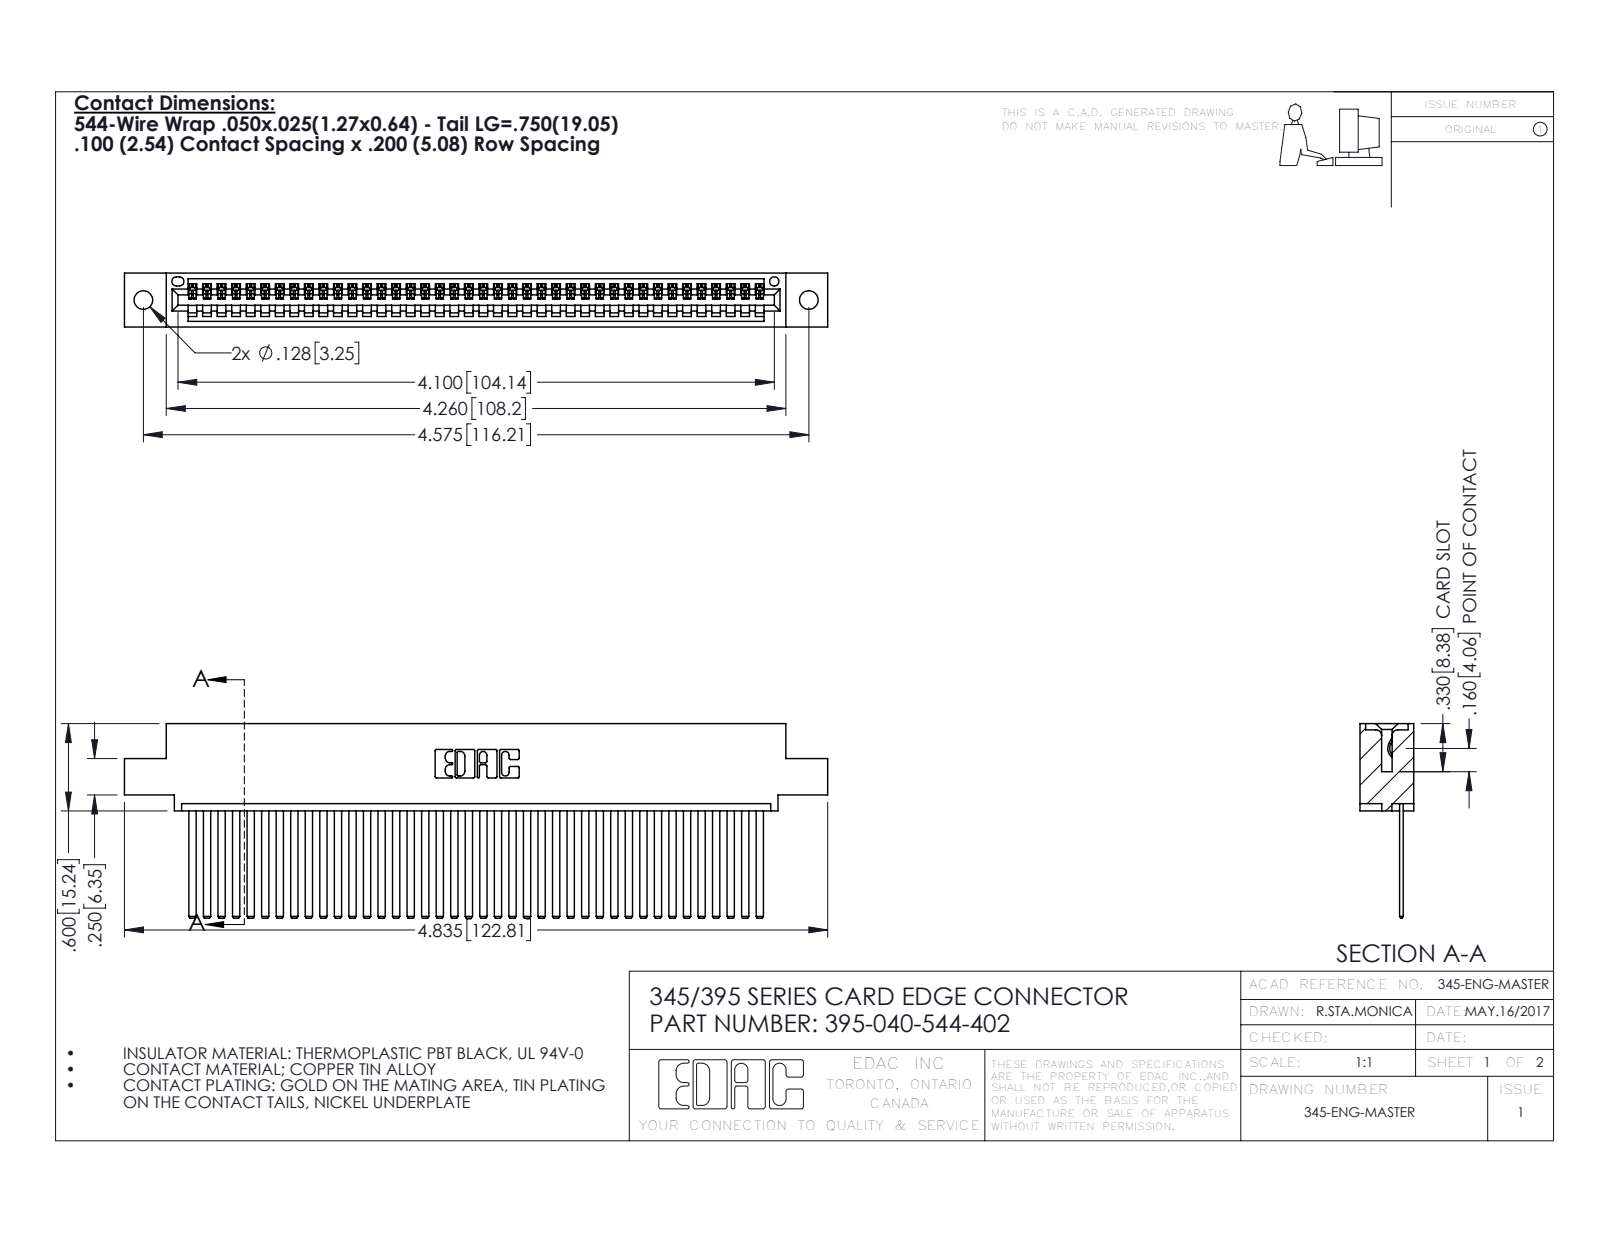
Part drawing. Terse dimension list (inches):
name: 395-040-544-402; 345 Part_0.110 Offset - 0.128 Dia; 345-292-001_345-293-144
written by: SolidWorks 2016 (CONFIG_CONTROL_DESIGN)
unit: in
bodies: 41 solids, 2210 faces (1524 planar, 686 cylindrical, 0 other)
size: 4.835 × 1.337 × 0.37
volume: 0.732 in³; area: 26.54 in²
holes: 2× ⌀0.128, 1× ⌀0.064
rounds: 80× R0.006, 22× R0.01, 6× R0.007, 6× R0.031, 3× R0.026, 2× R0.031, 2× R0.04, 1× R0.014
face distances: 0.072, 0.298, 0.025, 0.098, 0.272, 0.37, 0.2, 0.225, 0.149, 0.072
hole spacings: 0.27, 4.339, 4.575
